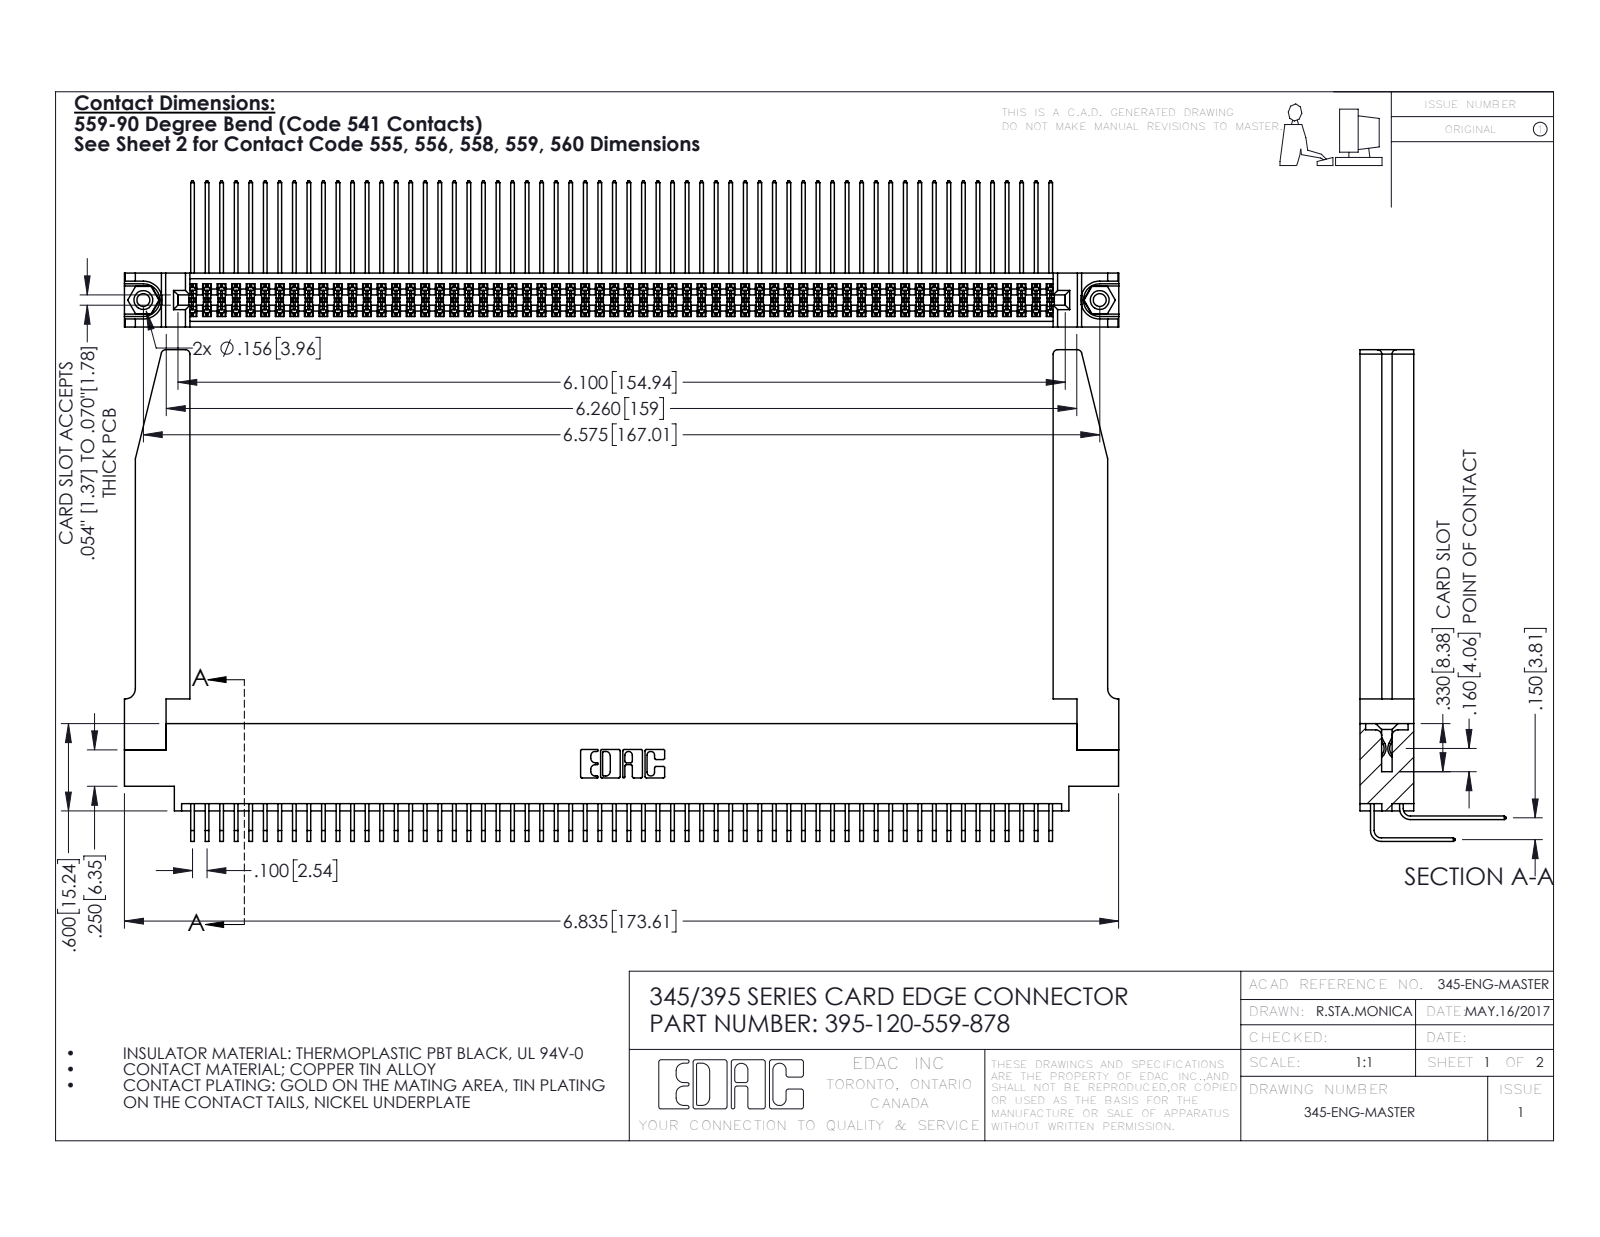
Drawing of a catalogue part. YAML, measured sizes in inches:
part_name: "345-292-001_558 559 Tail - 1; 345-292-001_559 Tail - 2; 395-120-559-878; 345-220-078_345-220-078 (+2 more)"
step_written_by: "SolidWorks 2016 (CONFIG_CONTROL_DESIGN)"
units: inches
bodies: {solids: 125, faces: 6604, planar: 4426, cylindrical: 2126, other: 52}
overall_size: [6.836, 3.379, 1.005]
volume: 1.549
surface_area: 56.76
round_holes:
  - {diameter: 0.089, count: 2}
  - {diameter: 0.125, count: 2}
  - {diameter: 0.156, count: 2}
  - {diameter: 0.064, count: 1}
round_bosses_or_shafts:
  - {diameter: 0.155, count: 2}
partial_cylinders:
  - {radius: 0.006, count: 180}
  - {radius: 0.01, count: 22}
  - {radius: 0.03, count: 8}
  - {radius: 0.007, count: 6}
  - {radius: 0.031, count: 6}
  - {radius: 0.026, count: 3}
  - {radius: 0.014, count: 2}
  - {radius: 0.019, count: 2}
face_to_face_distances: [0.072, 0.37, 0.298, 0.098, 0.272, 0.025, 0.2, 0.225, 0.15, 0.175]
hole_center_spacings: [0.27, 6.339, 6.575]
